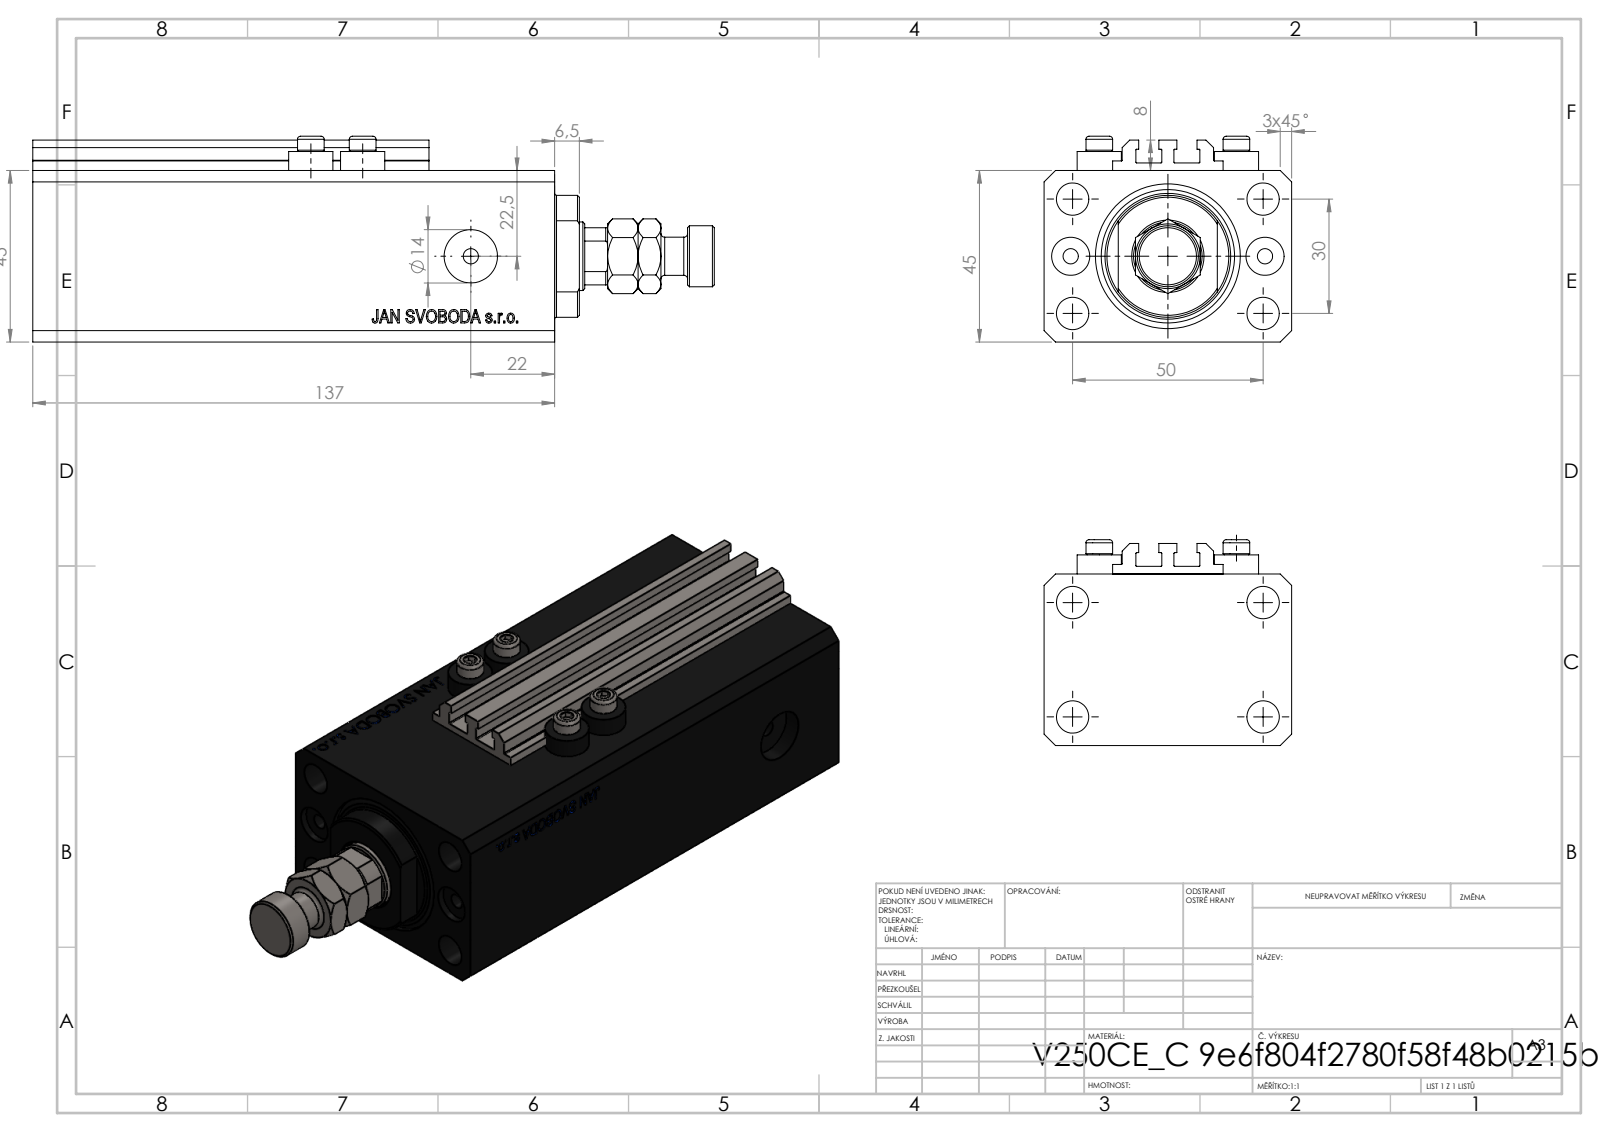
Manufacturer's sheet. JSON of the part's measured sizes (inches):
{"part_name": "V250CE_VC_C; MFA; ALLEN BOLT V250CE; V250CE_C_Body (+1 more)", "step_written_by": "SolidWorks 2019 (CONFIG_CONTROL_DESIGN)", "units": "inches", "bodies": {"solids": 9, "faces": 1085, "planar": 519, "cylindrical": 90, "other": 476}, "overall_size": [7.043, 2.559, 2.126], "volume_in3": 22.67, "surface_area_in2": 147, "round_holes": [[0.157, 8], [0.335, 5], [0.394, 2], [0.551, 2], [0.709, 1], [0.984, 1], [1.496, 1]], "round_bosses_or_shafts": [[0.457, 4], [0.276, 4], [0.63, 1], [0.394, 1]], "partial_cylinders_radius": [[0.008, 10], [0.335, 1], [0.63, 1]], "face_to_face_distances": [1.772, 2.559, 1.85, 4.406, 5.394, 0.988, 0.098, 0.079, 0.236, 0.394], "hole_center_spacings": [0.591, 1.148, 2.074, 0.535, 1.004, 1.181, 1.417, 1.515]}
